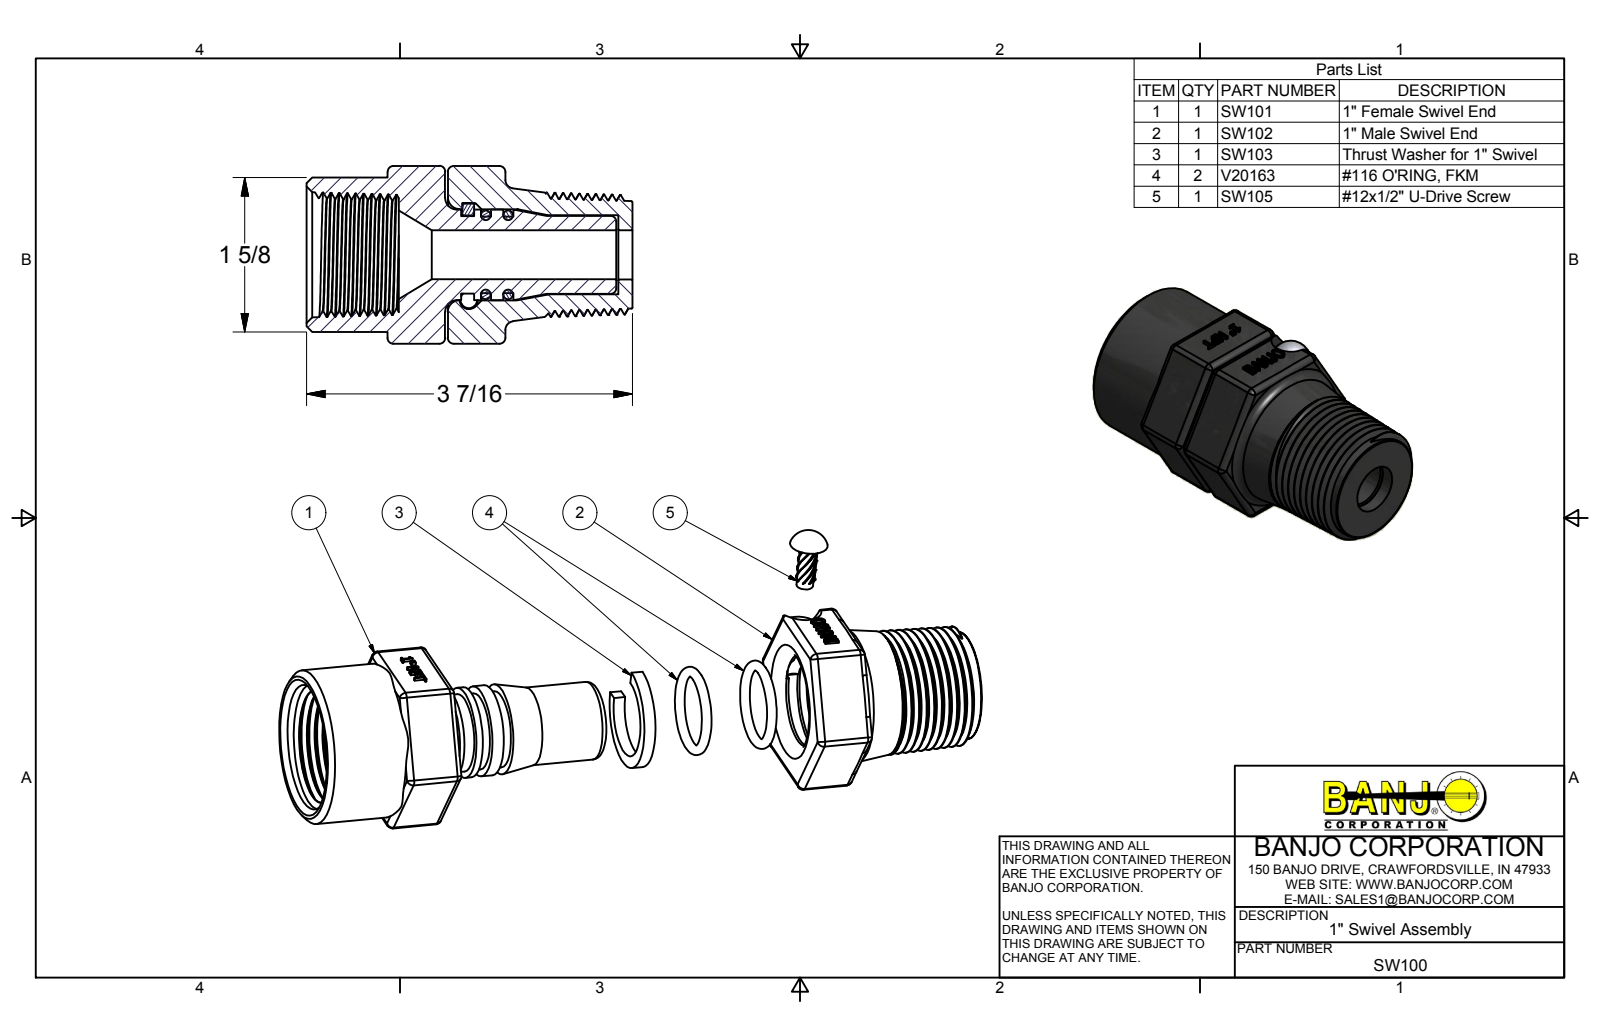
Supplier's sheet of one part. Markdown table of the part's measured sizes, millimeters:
| quantity | value |
| --- | --- |
| part name | SW101; SWX102; SW102; SW103 (+3 more) |
| STEP written by | Autodesk Inventor 2014 (AUTOMOTIVE_DESIGN) |
| units | millimeters |
| bodies | 6 solids, 497 faces (219 planar, 85 cylindrical, 193 other) |
| overall size | 87.94 × 47.92 × 43.43 |
| volume | 74 335 mm³ |
| surface area | 33 470 mm² |
| round holes (diameter × count) | 4.98 × 1, 10.49 × 1, 13.21 × 1, 13.31 × 1, 21.34 × 1, 24.56 × 1, 28.04 × 1 |
| round bosses / shafts (diameter × count) | 41.66 × 1, 24.41 × 1, 21.06 × 1, 20.93 × 1, 20.6 × 1, 5.13 × 1, 4.47 × 1 |
| partial cylindrical surfaces (radius × count) | 1.52 × 18, 1.59 × 18, 0.33 × 8, 8.86 × 1, 10.06 × 1, 10.62 × 1, 13.79 × 1, 16.76 × 1 |
| main face-to-face distances | 41.9, 49.78, 0.81, 50.59, 4.7, 3.89, 45.89, 7.87, 7.06, 3.17 |
